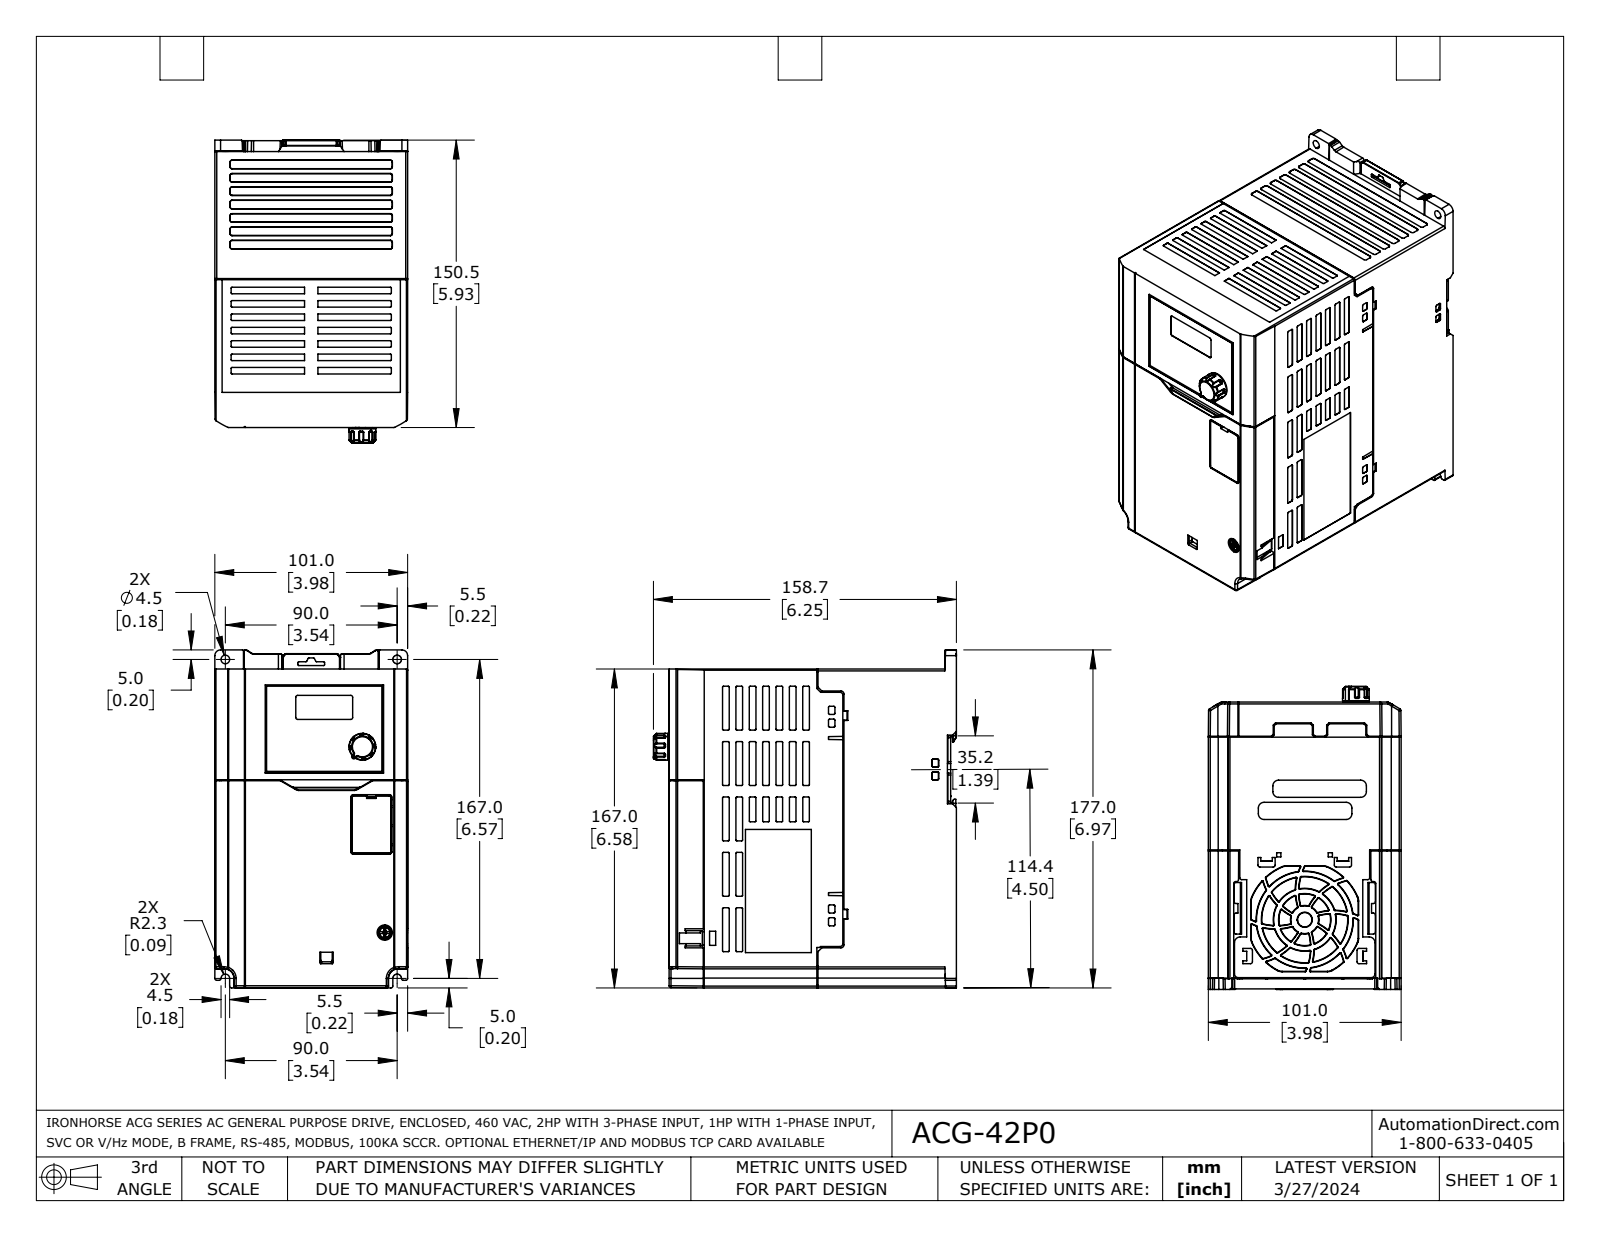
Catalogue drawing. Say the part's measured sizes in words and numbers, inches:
The part is named "ACG-42P0". Its 3-D file was written by "SolidWorks 2021 (AUTOMOTIVE_DESIGN)". It is 4 solids with 4588 faces: 1880 planar, 1198 cylindrical and 1510 other. Overall it measures 6.969 by 6.248 by 3.976 inches. Its volume is 150.5 cubic inches and its surface area 234.5 square inches. Round holes: 4 of diameter 0.134, 1 of diameter 0.039, 1 of diameter 0.276, 1 of diameter 0.472. Round bosses or shafts: 1 of diameter 0.551, 1 of diameter 0.543, 1 of diameter 0.236. Partial cylindrical surfaces (rounded edges, fillets, slot ends): 347 of radius 0.008, 240 of radius 0.02, 95 of radius 0.039, 38 of radius 0.018, 24 of radius 0.012, 17 of radius 0.031, 12 of radius 0.118, 4 of radius 0.016. The main face-to-face distances are 3.976, 5.807, 3.975, 6.575, 5.795, 6.573, 0.106, 5.913, 0.118, 0.098. The hole center spacings are 3.496, 4.882, 6.005, 0.276, 0.491, 0.928, 1.202, 2.754.
